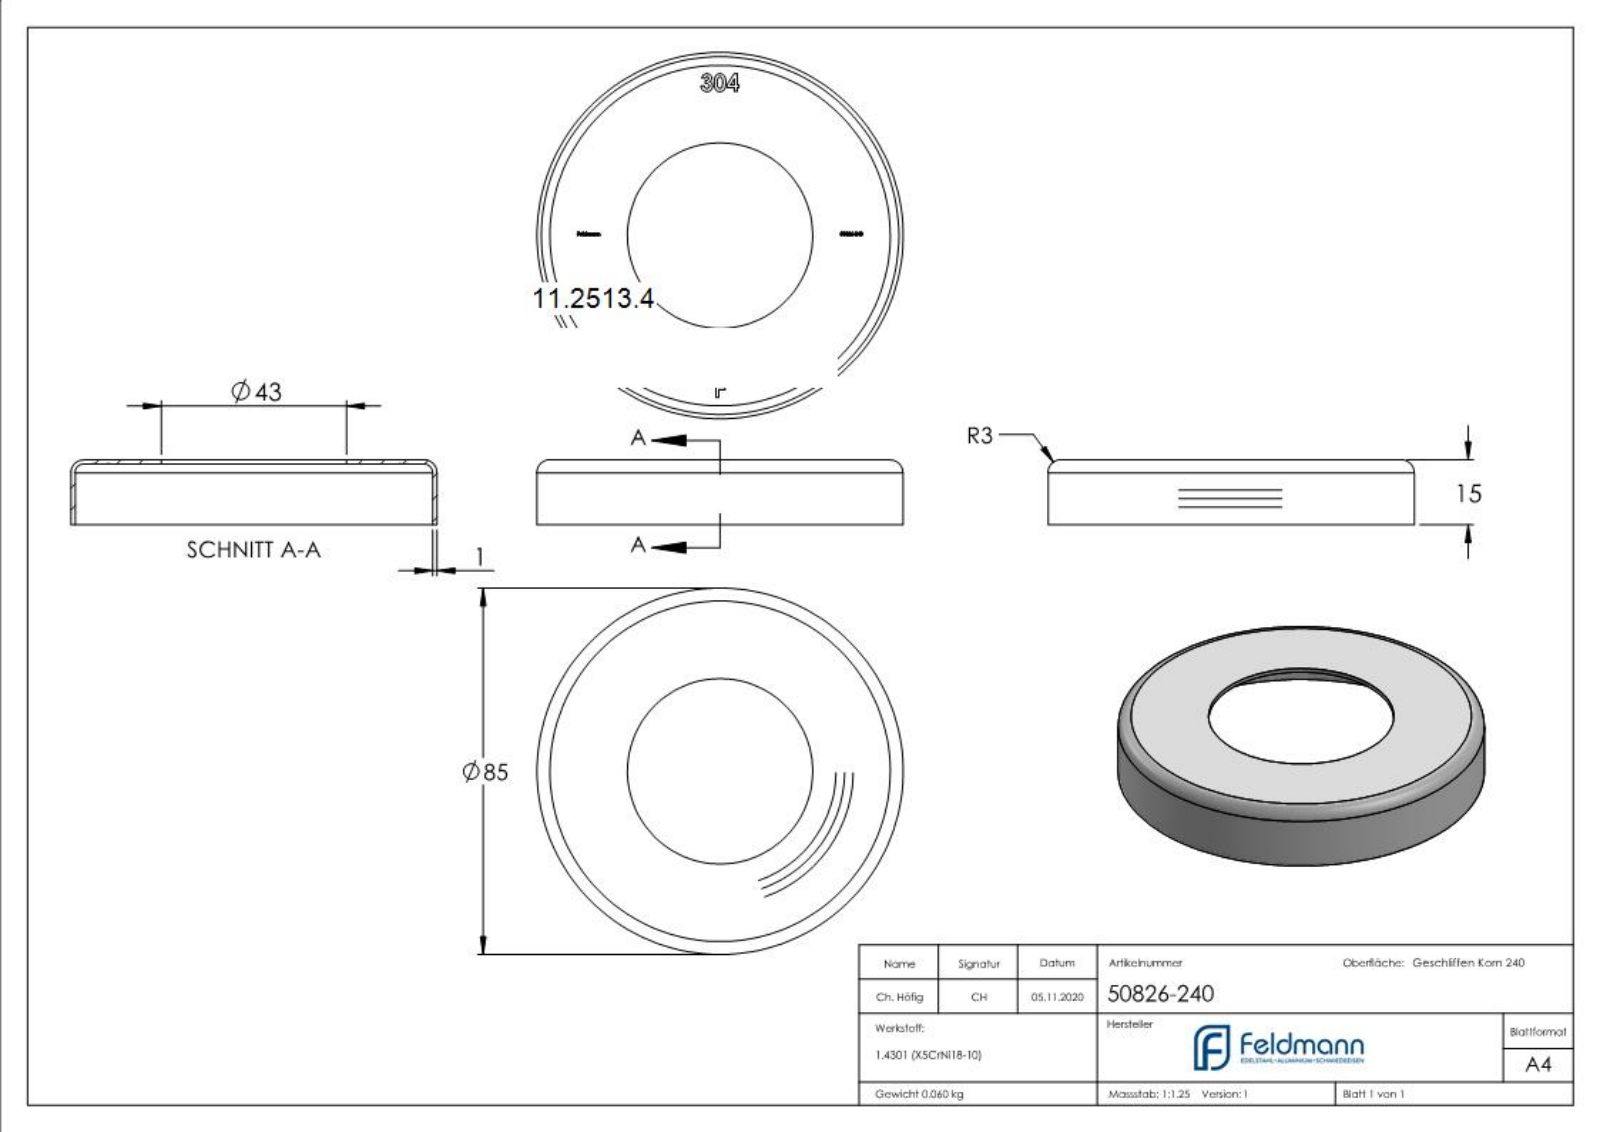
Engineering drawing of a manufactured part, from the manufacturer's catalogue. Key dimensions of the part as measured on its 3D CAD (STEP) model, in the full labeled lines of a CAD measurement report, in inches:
Part name (STEP PRODUCT): 50826-240
STEP written by: SolidWorks 2018 (CONFIG_CONTROL_DESIGN)
Units: inches
Bodies: 1 solid, 301 faces (154 planar, 6 cylindrical, 141 other)
Overall size (bounding box): 3.346 × 3.346 × 0.591
Volume: 0.465 in³ · Surface area: 24.3 in²
Round holes (diameter × count): ⌀1.693 ×1, ⌀3.268 ×1
Round bosses / shafts (diameter × count): ⌀3.346 ×1
Main face-to-face distances: 0.039, 0.551, 0.591, 0.555, 0.035, 0.028, 0.197, 1.41, 0.169, 0.023
